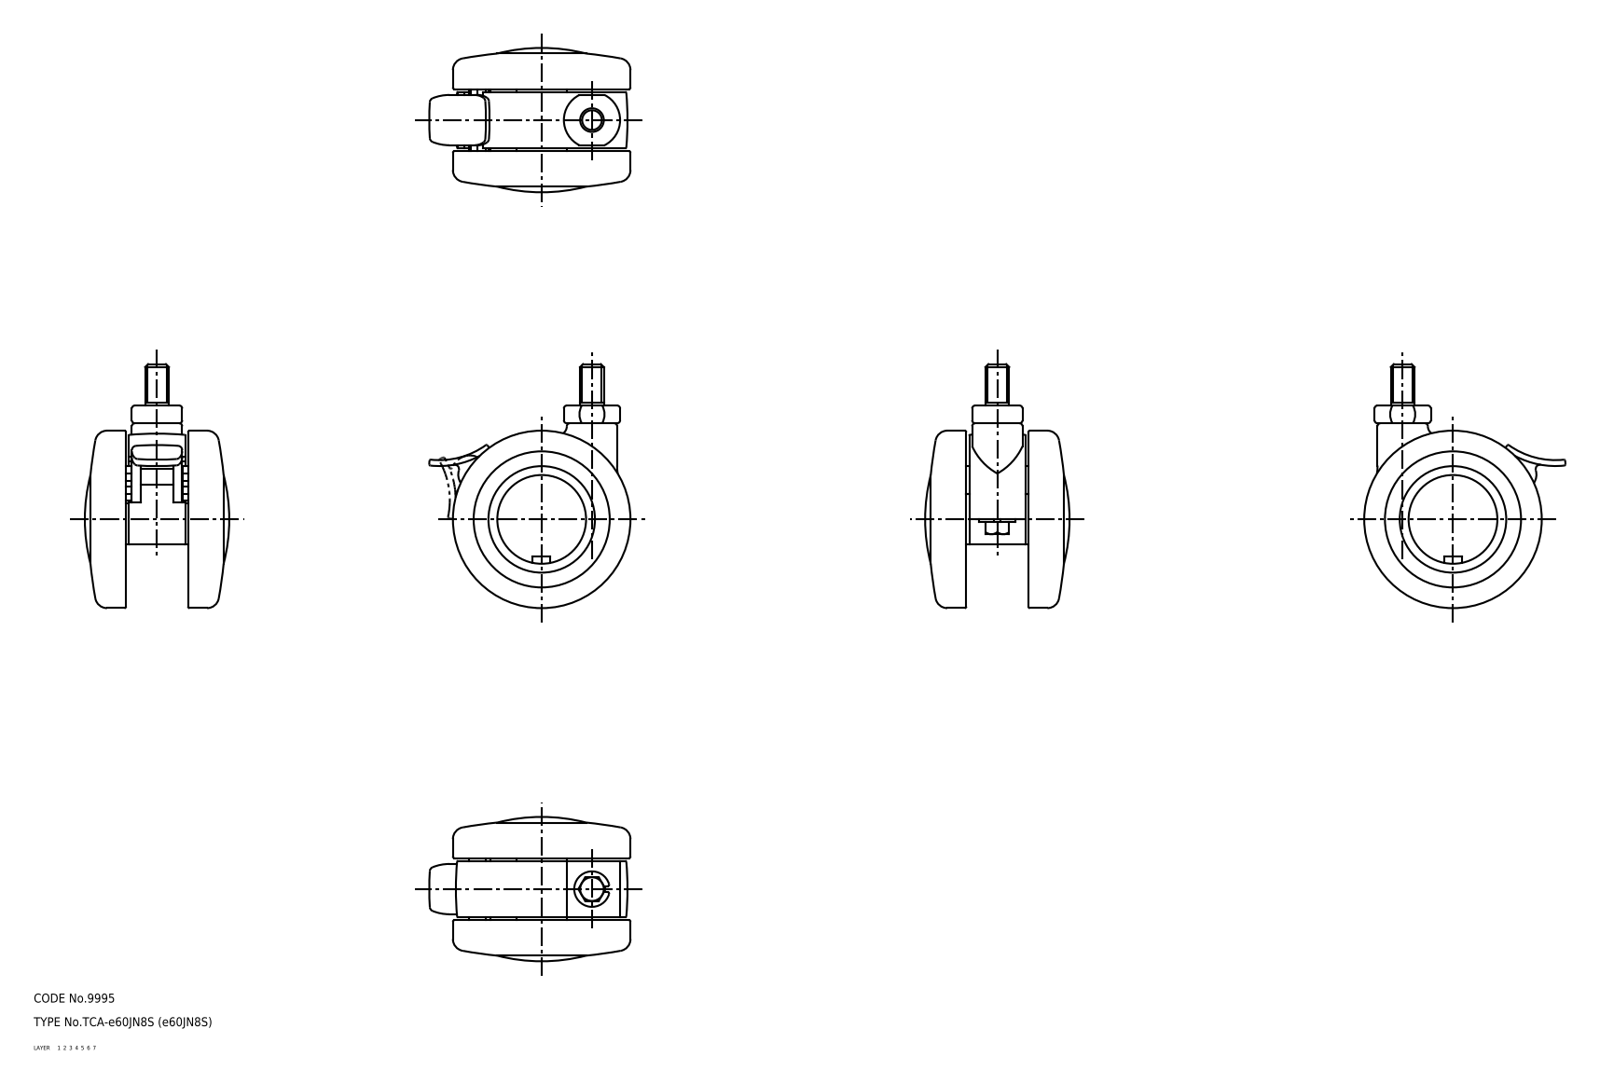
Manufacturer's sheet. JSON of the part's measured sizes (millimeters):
{"part_name": "lever; wheel_mr; wheel; main shaft (+1 more)", "step_written_by": "CADfix (AUTOMOTIVE_DESIGN)", "units": "millimeters", "bodies": {"solids": 5, "faces": 208, "planar": 0, "cylindrical": 0, "other": 208}, "overall_size": [82.5, 68, 48.81], "volume_mm3": 85644, "surface_area_mm2": 32565}
